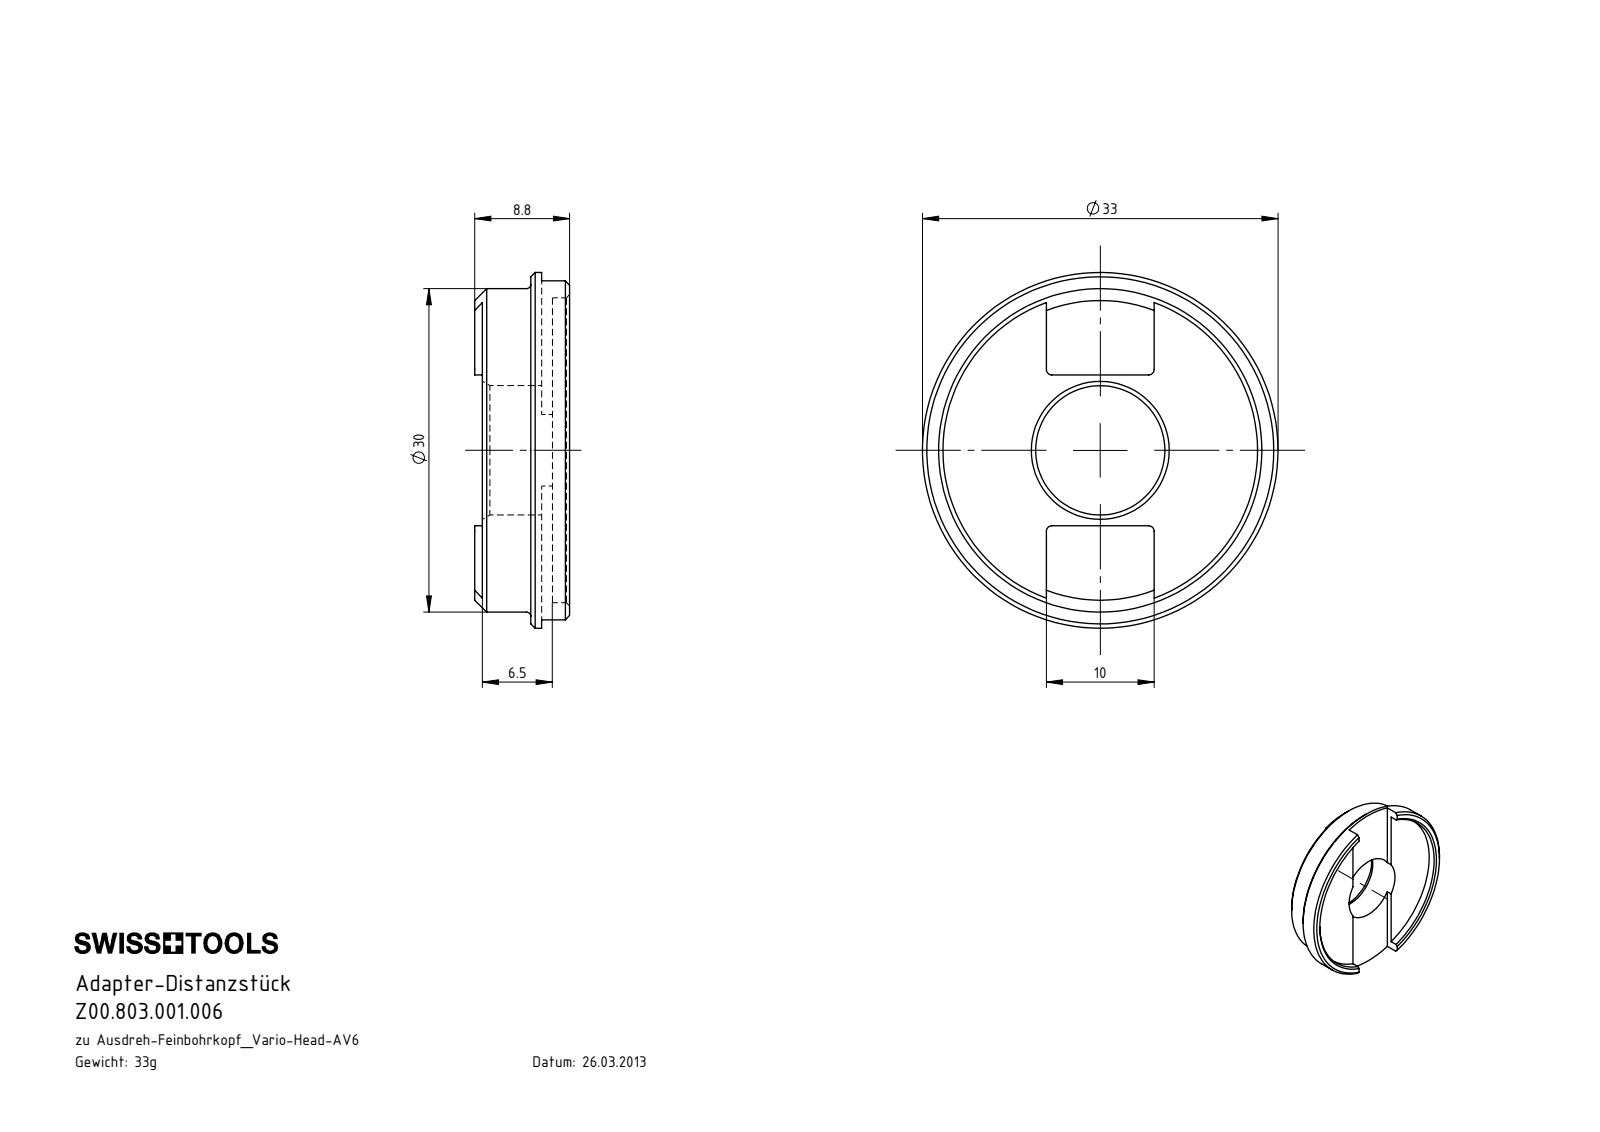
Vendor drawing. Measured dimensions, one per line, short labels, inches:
name: Z00.803.001.006
written by: SolidWorks 2022 (CONFIG_CONTROL_DESIGN)
unit: in
bodies: 1 solid, 47 faces (20 planar, 13 cylindrical, 14 other)
size: 1.299 × 1.299 × 0.346
volume: 0.256 in³; area: 3.966 in²
holes: 1× ⌀0.472, 1× ⌀1.181
bosses: 1× ⌀1.299
rounds: 4× R0.02
face distances: 0.256, 0.039, 0.217, 0.028, 0.244, 0.283, 0.205, 0.177, 0.079, 0.346
